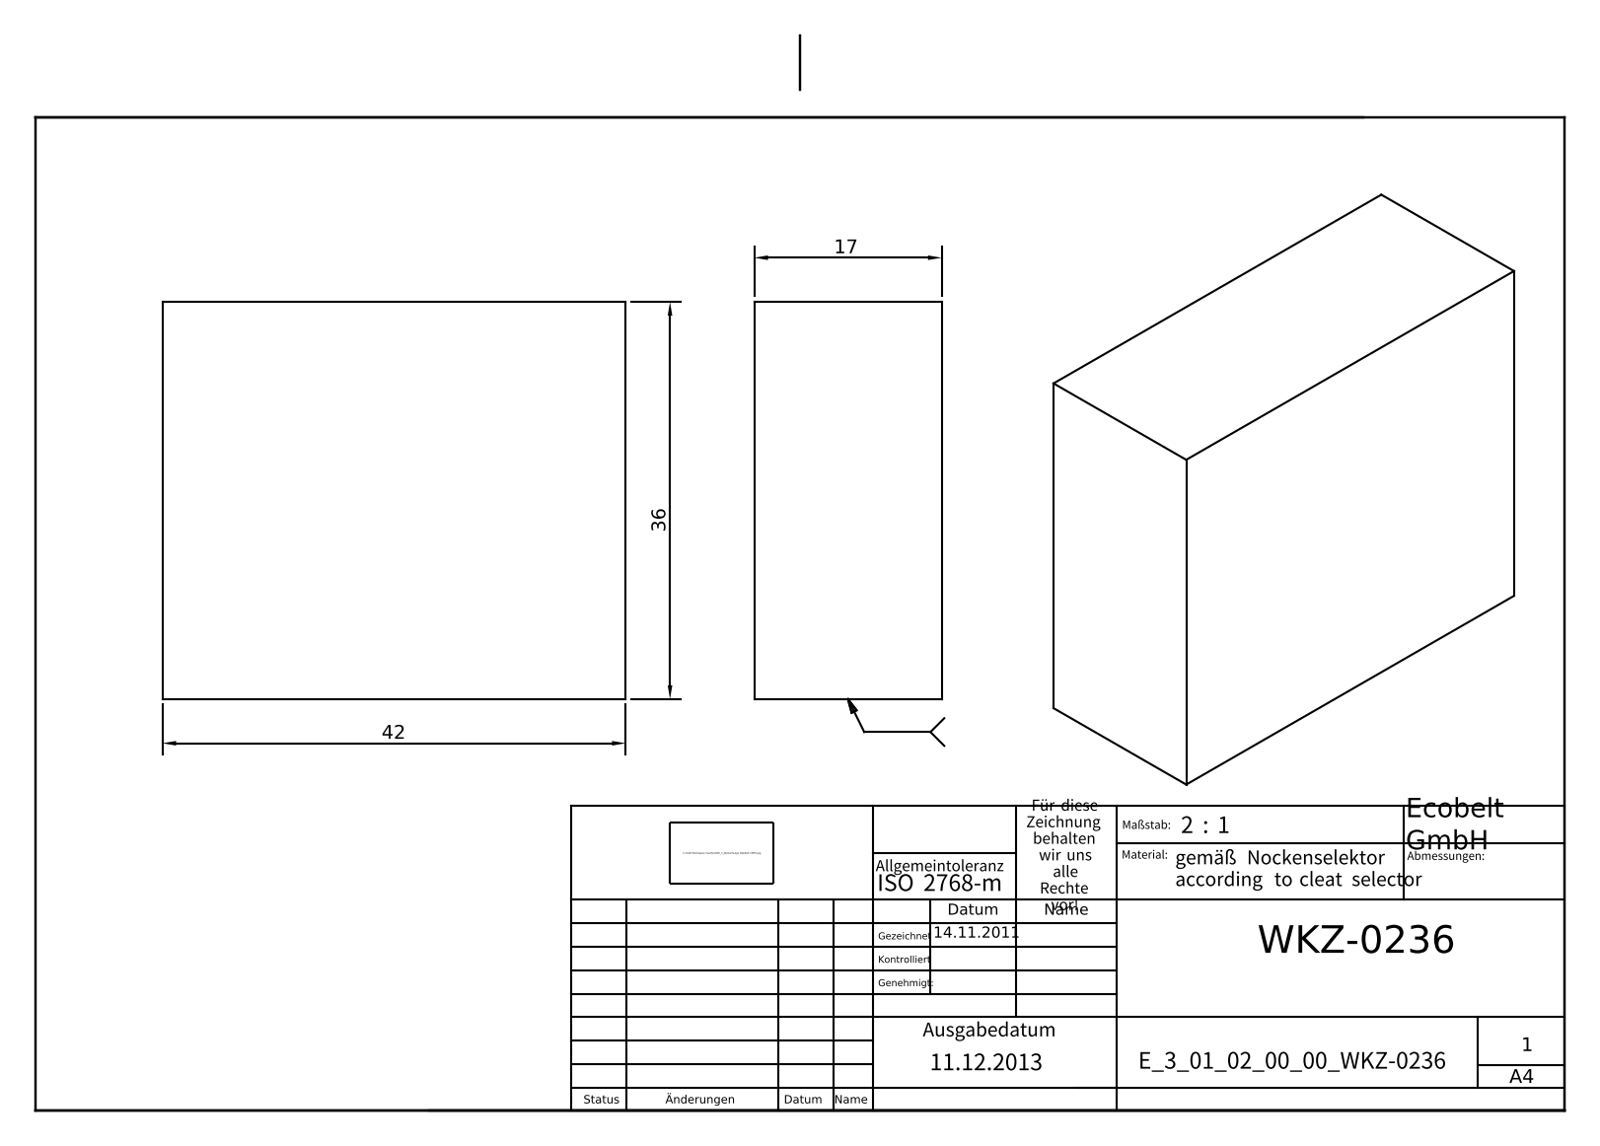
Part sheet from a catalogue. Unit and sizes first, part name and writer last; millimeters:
Units: millimetres
Overall size (bounding box): 42 × 36 × 17
Main face-to-face distances: 17, 36, 42
Volume: 25 704 mm³ · Surface area: 5 676 mm²
Bodies: 1 solid, 6 faces (6 planar, 0 cylindrical, 0 other)
Part name (STEP PRODUCT): E_3_01_02_00_00_WKZ-0236
STEP written by: Autodesk Inventor 2021 (AUTOMOTIVE_DESIGN)
